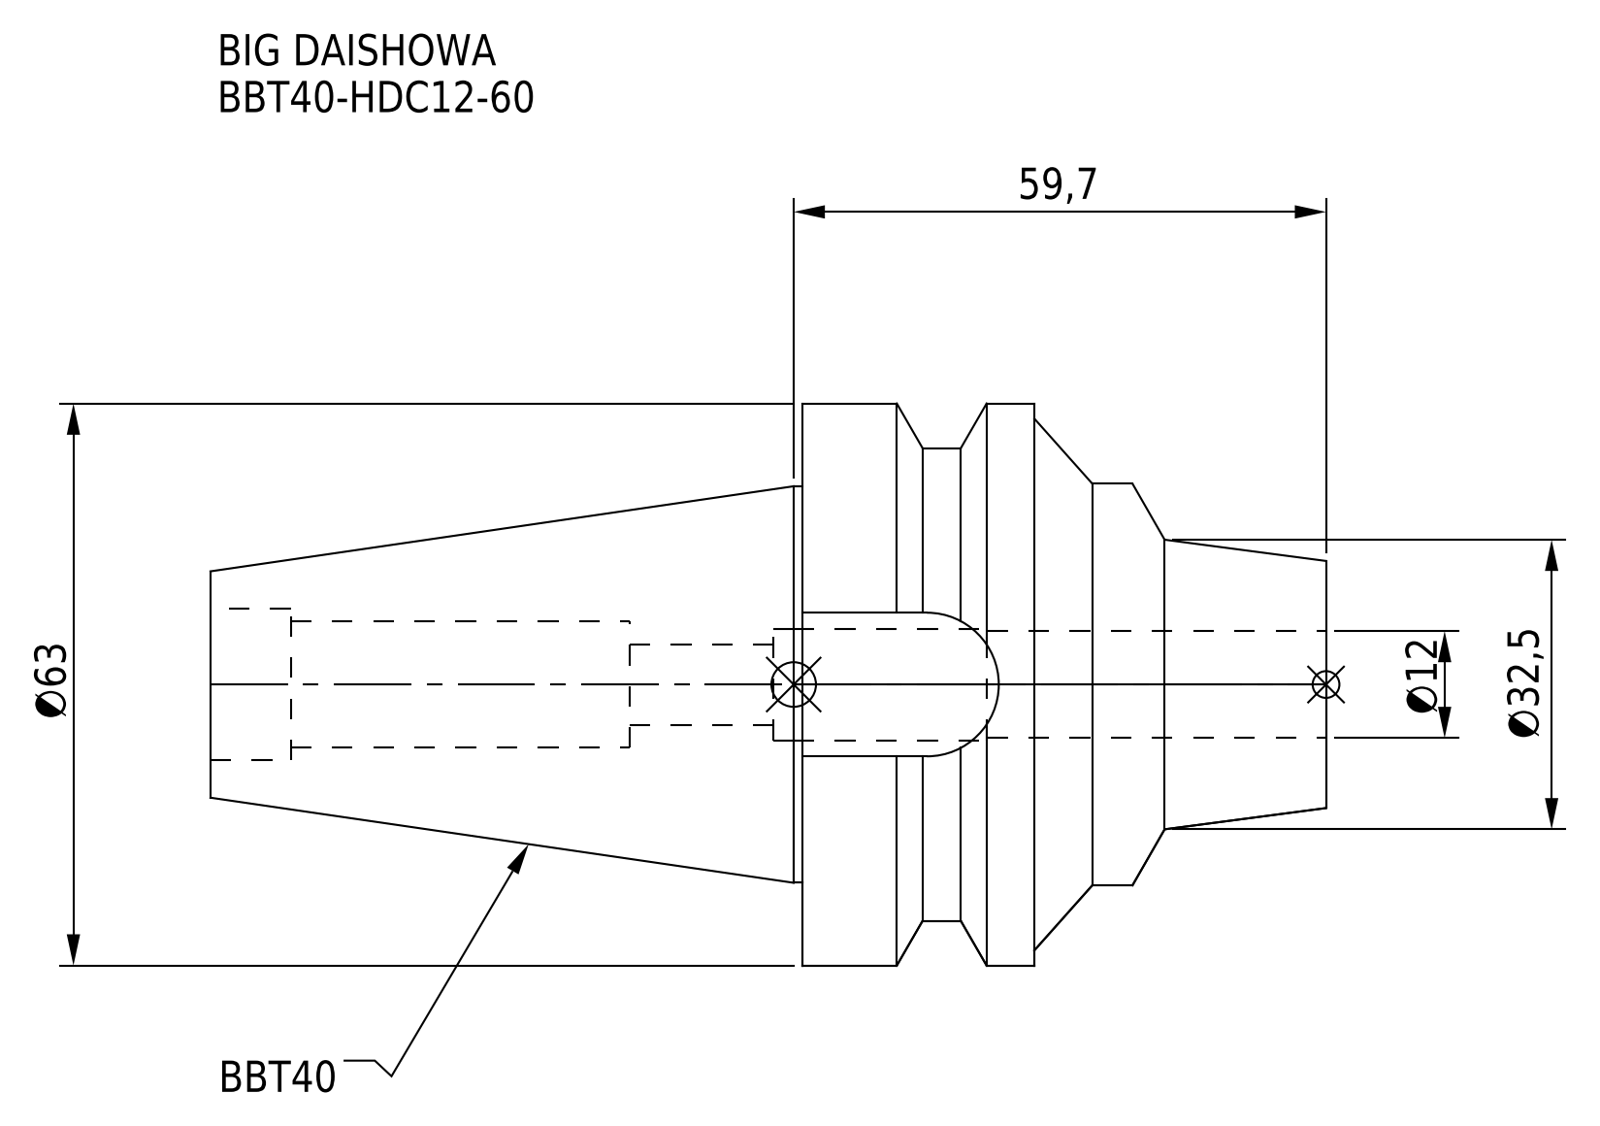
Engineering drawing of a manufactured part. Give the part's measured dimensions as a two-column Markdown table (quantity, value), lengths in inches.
| quantity | value |
| --- | --- |
| part name | BBT40-HDC12-60 |
| STEP written by | CREO PARAMETRIC BY PTC INC, 2016380 (AUTOMOTIVE_DESIGN) |
| units | inches |
| bodies | 1 solid, 50 faces (14 planar, 24 cylindrical, 12 other) |
| overall size | 4.925 × 2.48 × 2.48 |
| volume | 9.619 in³ |
| surface area | 40.87 in² |
| round holes (diameter × count) | 0.354 × 1, 0.472 × 1, 0.492 × 1, 0.559 × 1, 0.669 × 1 |
| round bosses / shafts (diameter × count) | 2.48 × 1, 2.087 × 1, 1.772 × 1, 1.75 × 1 |
| partial cylindrical surfaces (radius × count) | 0.317 × 1 |
| main face-to-face distances | 2.311, 1.287, 1.024, 1.772, 4.925, 3.638, 2.614, 0.634, 3.075, 1.787 |
